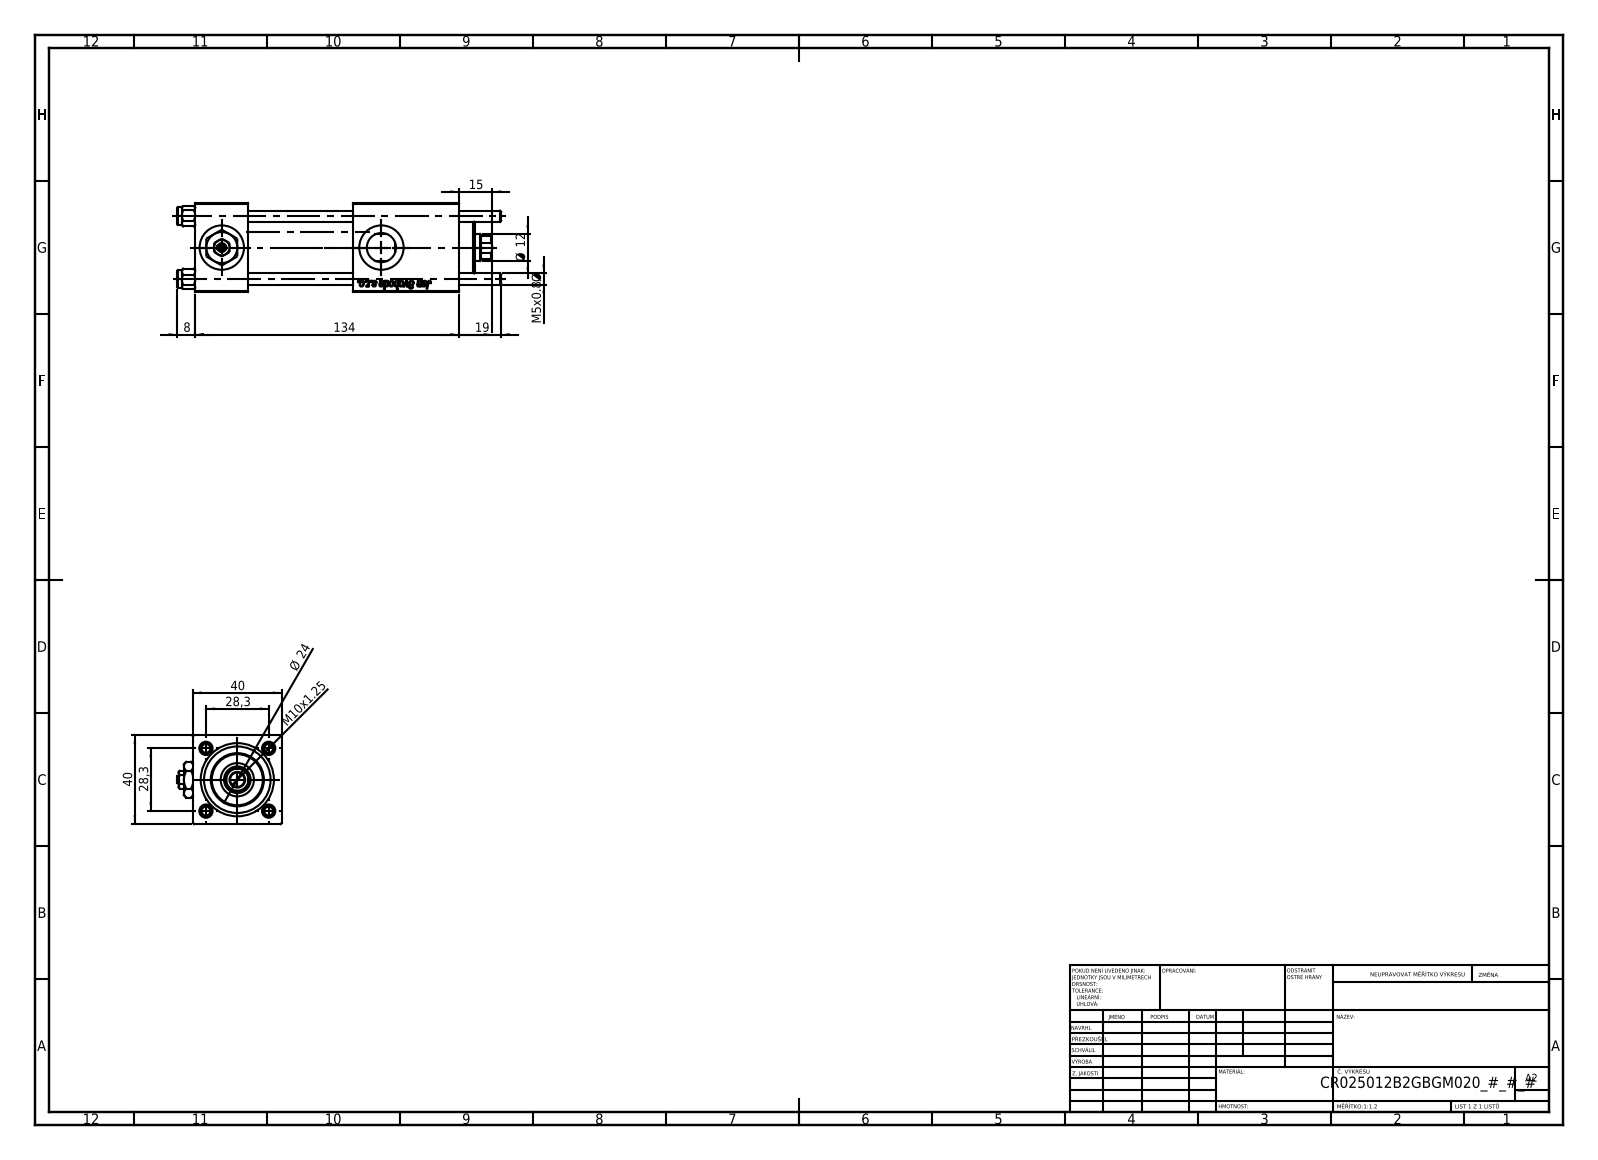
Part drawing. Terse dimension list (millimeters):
name: Zatka_pro_OIL_PORT; NUT_M5_B; V215_VC_A; V215CR_VCP_B (+2 more)
written by: SolidWorks 2019 (CONFIG_CONTROL_DESIGN)
unit: mm
bodies: 12 solids, 1208 faces (452 planar, 86 cylindrical, 670 other)
size: 146 × 47 × 40
volume: 144 131 mm³; area: 59 643 mm²
holes: 4× ⌀5, 3× ⌀20, 2× ⌀7, 2× ⌀13.16, 1× ⌀6.5, 1× ⌀12, 1× ⌀15, 1× ⌀25, 1× ⌀30
bosses: 4× ⌀8, 1× ⌀31, 1× ⌀24
rounds: 1× R5.5
face distances: 40, 24, 90.3, 66.3, 119, 47, 71, 19.3, 95, 48
hole spacings: 20.01, 28.3, 40.02, 72
